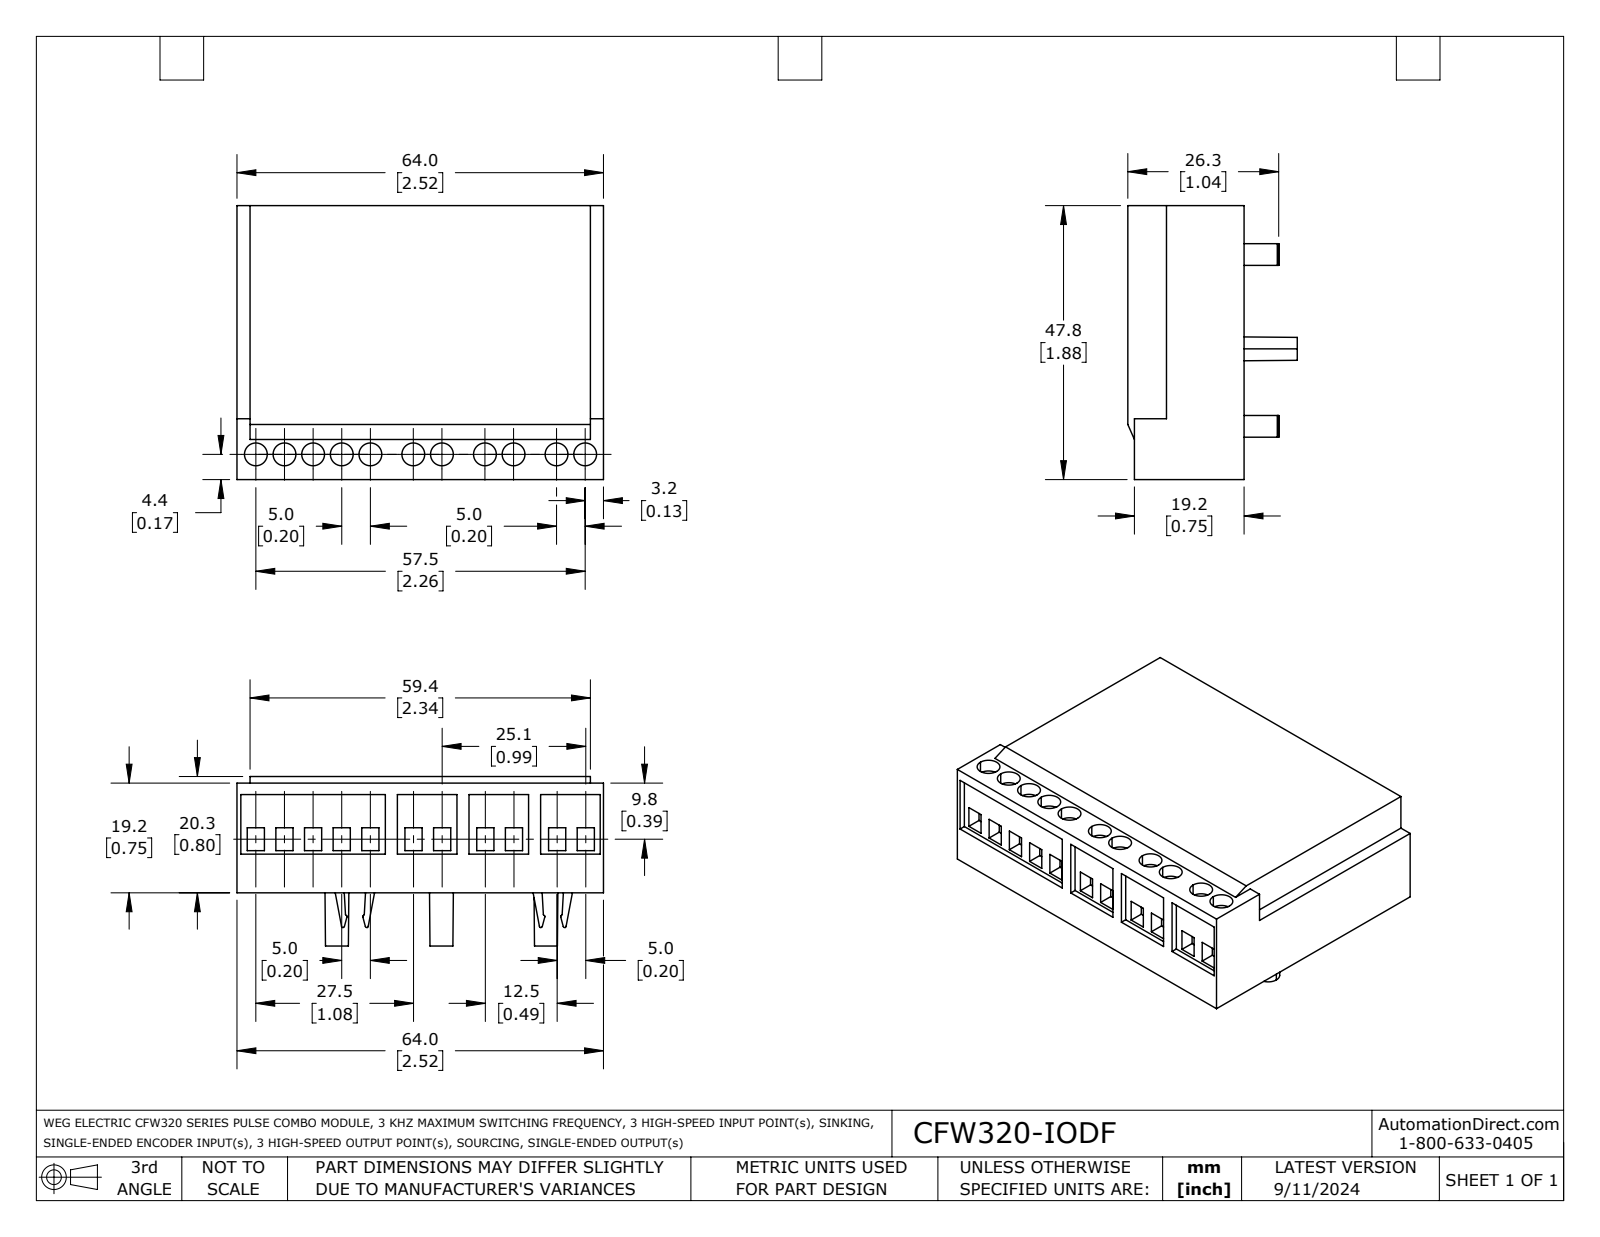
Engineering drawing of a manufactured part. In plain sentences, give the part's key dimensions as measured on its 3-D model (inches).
The part is named "CFW320 IODF". Its 3-D file was written by "SolidWorks 2021 (AUTOMOTIVE_DESIGN)". It is 1 solid with 206 faces: 162 planar, 22 cylindrical and 22 other. Overall it measures 2.52 by 1.883 by 1.165 inches. Its volume is 3.553 cubic inches and its surface area 19.05 square inches. Round holes: 11 of diameter 0.157. The main face-to-face distances are 0.799, 1.883, 2.52, 0.09, 2.43, 0.042, 1.841, 0.165, 0.634, 0.754. The hole center spacings are 0.197, 0.493, 0.394, 0.296, 0.492, 0.591, 0.689, 0.689.
